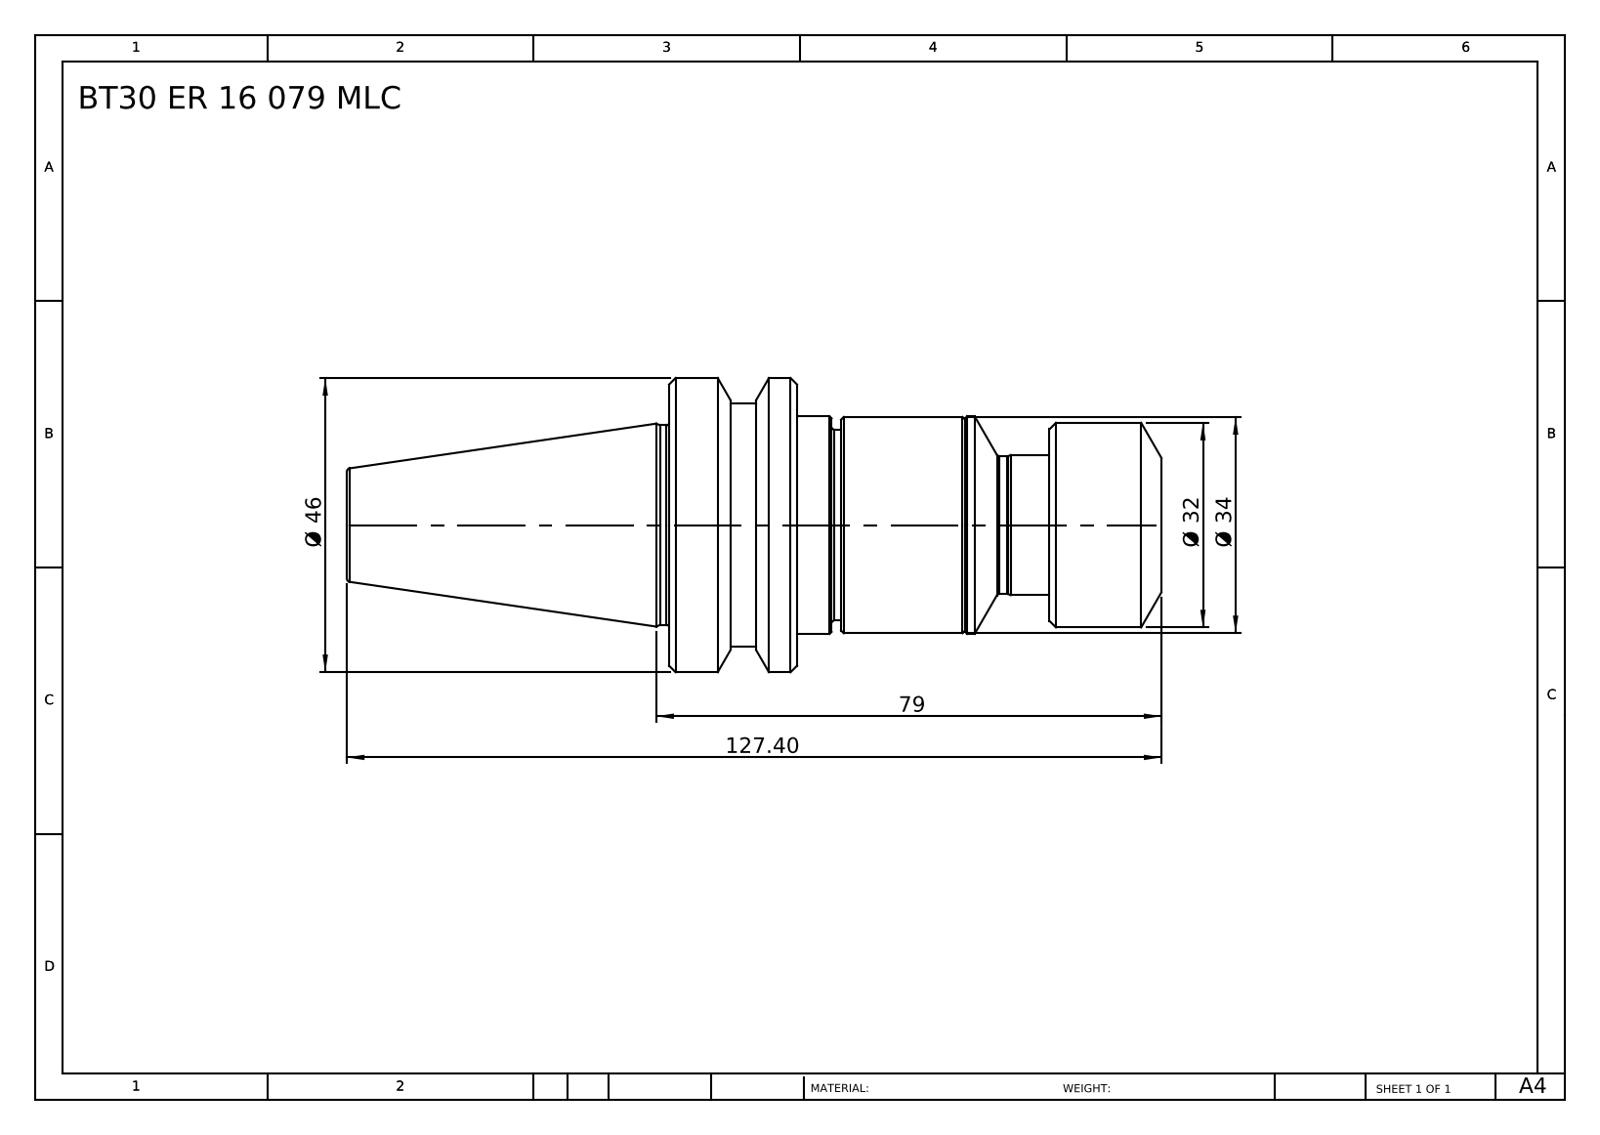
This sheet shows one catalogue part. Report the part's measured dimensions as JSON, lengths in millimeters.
{"part_name": "BT30 ER 16 079 MLC", "step_written_by": "SolidWorks 2014 (CONFIG_CONTROL_DESIGN)", "units": "millimeters", "bodies": {"solids": 1, "faces": 70, "planar": 10, "cylindrical": 22, "other": 38}, "overall_size": [127.4, 46, 46], "volume_mm3": 98568, "surface_area_mm2": 16300, "round_bosses_or_shafts": [[46, 1], [38, 1], [34, 1], [33.8, 1], [32, 1], [31.2, 1], [29.9, 1], [21.9, 1]], "face_to_face_distances": [20, 57, 77, 17.5, 39.5, 59.5, 127.4, 109.9, 70.4, 50.4]}
